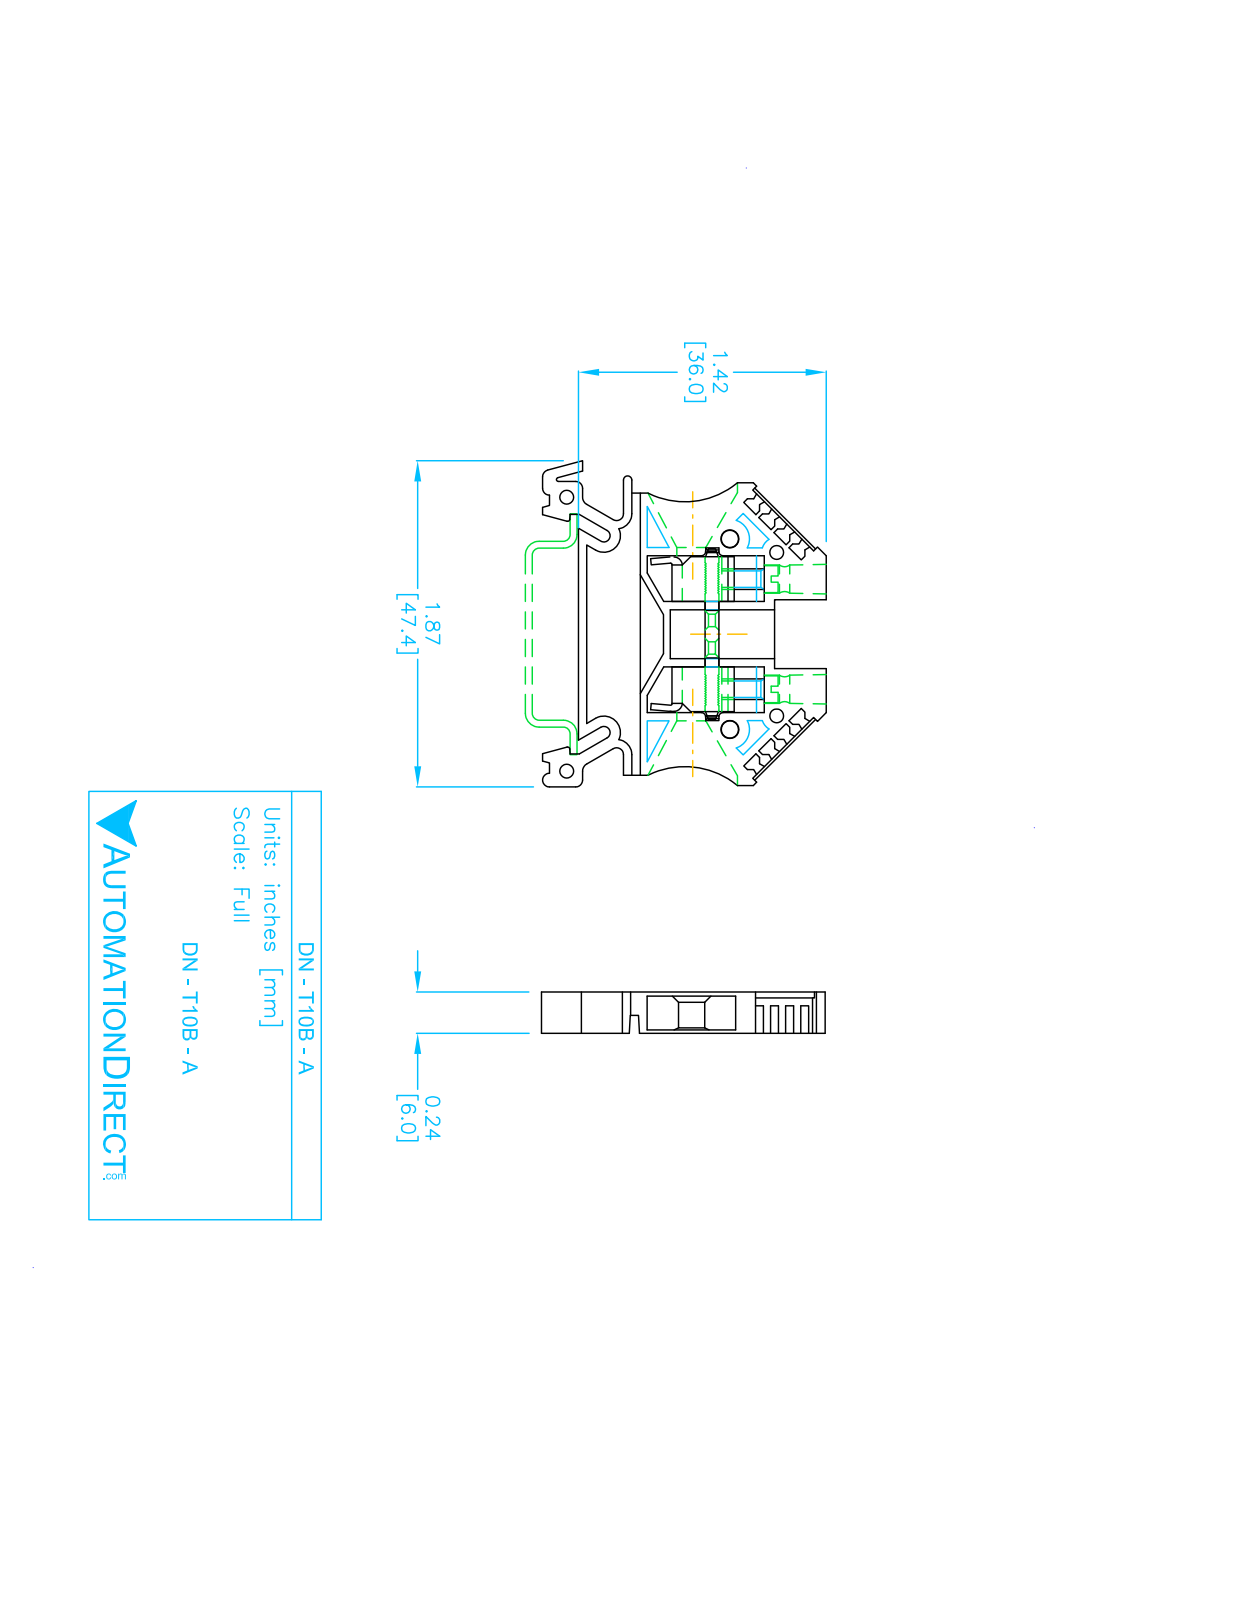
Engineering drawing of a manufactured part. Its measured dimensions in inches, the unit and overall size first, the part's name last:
Units: inches
Overall size (bounding box): 1.866 × 1.622 × 0.236
Round holes (diameter × count): ⌀0.079 ×2, ⌀0.172 ×2
Partial cylindrical surfaces — rounded edges, fillets, slot ends (radius × count): R0.039 ×7, R0.012 ×2, R0.035 ×2, R0.047 ×2, R0.087 ×2, R0.094 ×2, R0.472 ×2, R0.011 ×1
Main face-to-face distances: 0.228, 0.236, 0.142, 0.094, 0.047, 0.087, 0.134, 0.354, 0.071, 0.307
Hole centre spacings: 0.63, 1.567
Volume: 0.381 in³ · Surface area: 7.683 in²
Bodies: 1 solid, 181 faces (141 planar, 40 cylindrical, 0 other)
Part name (STEP PRODUCT): DN-T10B-A
STEP written by: SolidWorks 2017 (AUTOMOTIVE_DESIGN)
